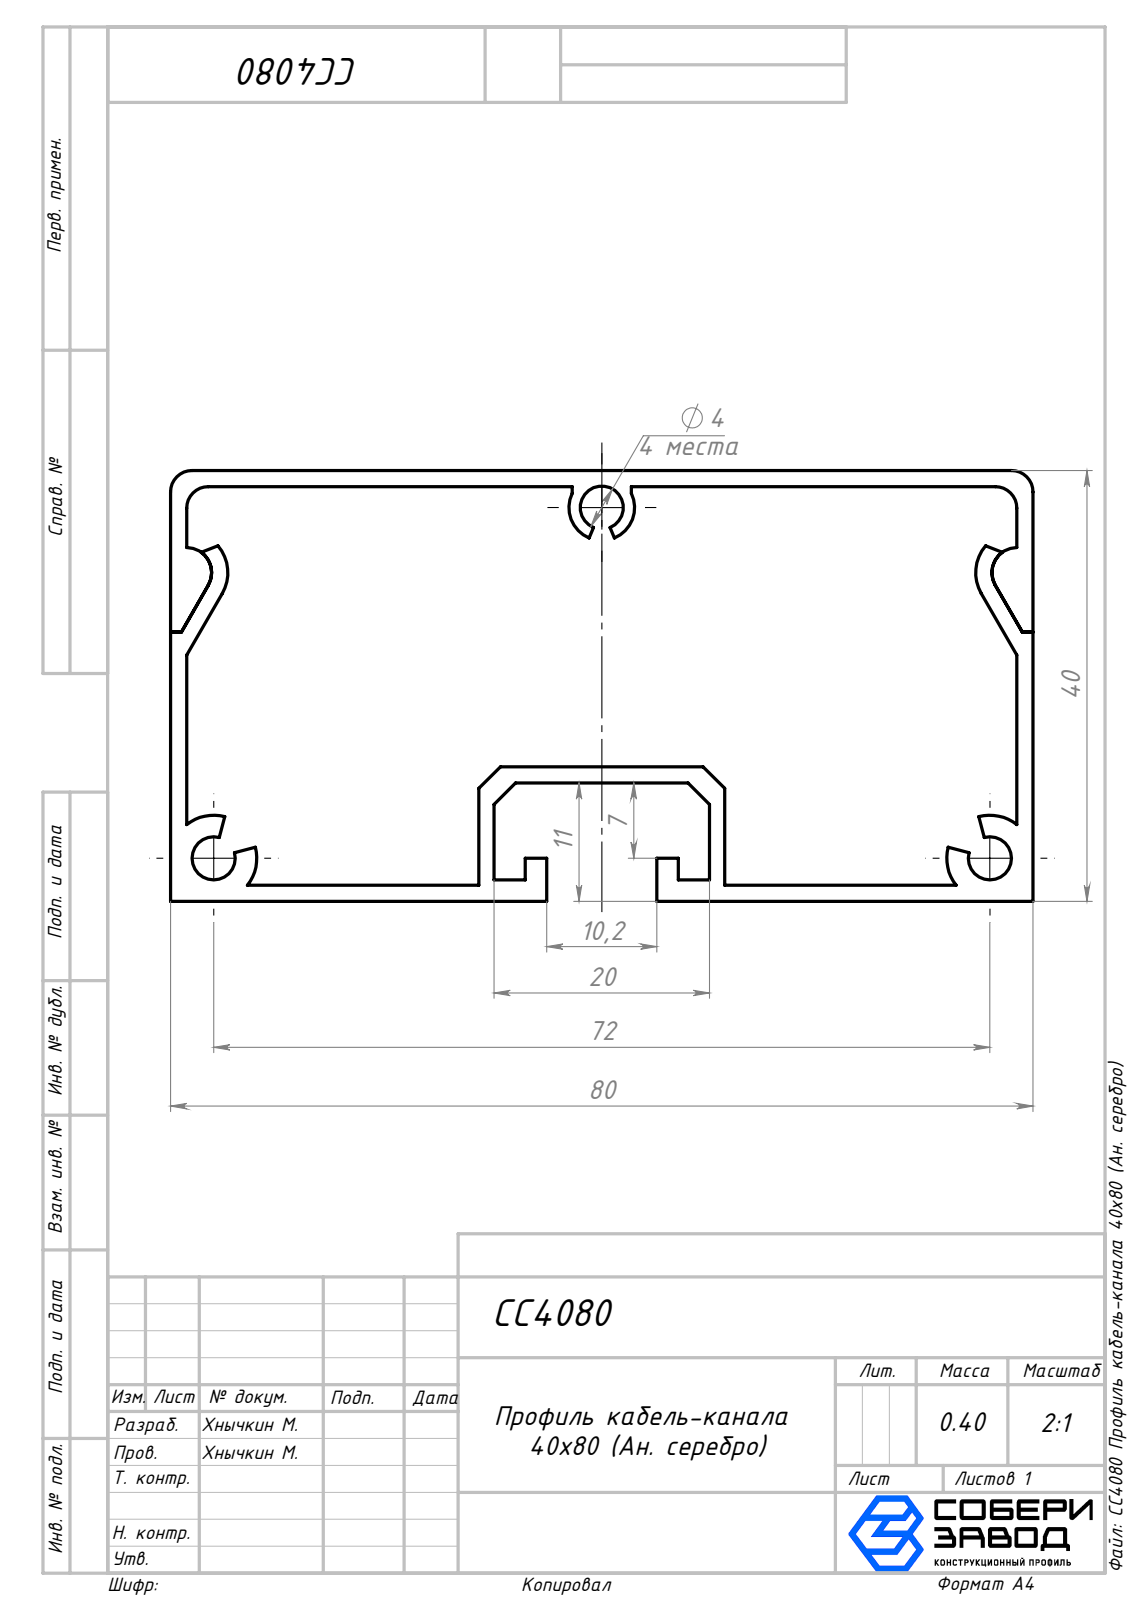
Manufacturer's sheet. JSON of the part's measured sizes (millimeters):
{"part_name": "CC4080 Профиль кабель-канала 40х80 (Ан. серебро); Алюм. кабель 40х80_00; Алюм. кабель, крышка 40х80_00", "step_written_by": "SolidWorks 2026 (AUTOMOTIVE_DESIGN)", "units": "millimeters", "bodies": {"solids": 2, "faces": 87, "planar": 57, "cylindrical": 30, "other": 0}, "overall_size": [100, 80, 39], "volume_mm3": 50749, "surface_area_mm2": 62308, "round_holes": [[4, 2], [3.2, 1]], "partial_cylinders_radius": [[2, 4], [2.35, 2], [3.85, 2], [4, 2], [3.05, 1]], "face_to_face_distances": [1.5, 37.5, 39, 36, 80, 78.5, 11, 26.5, 12.5, 25], "hole_center_spacings": [47.87, 72]}
